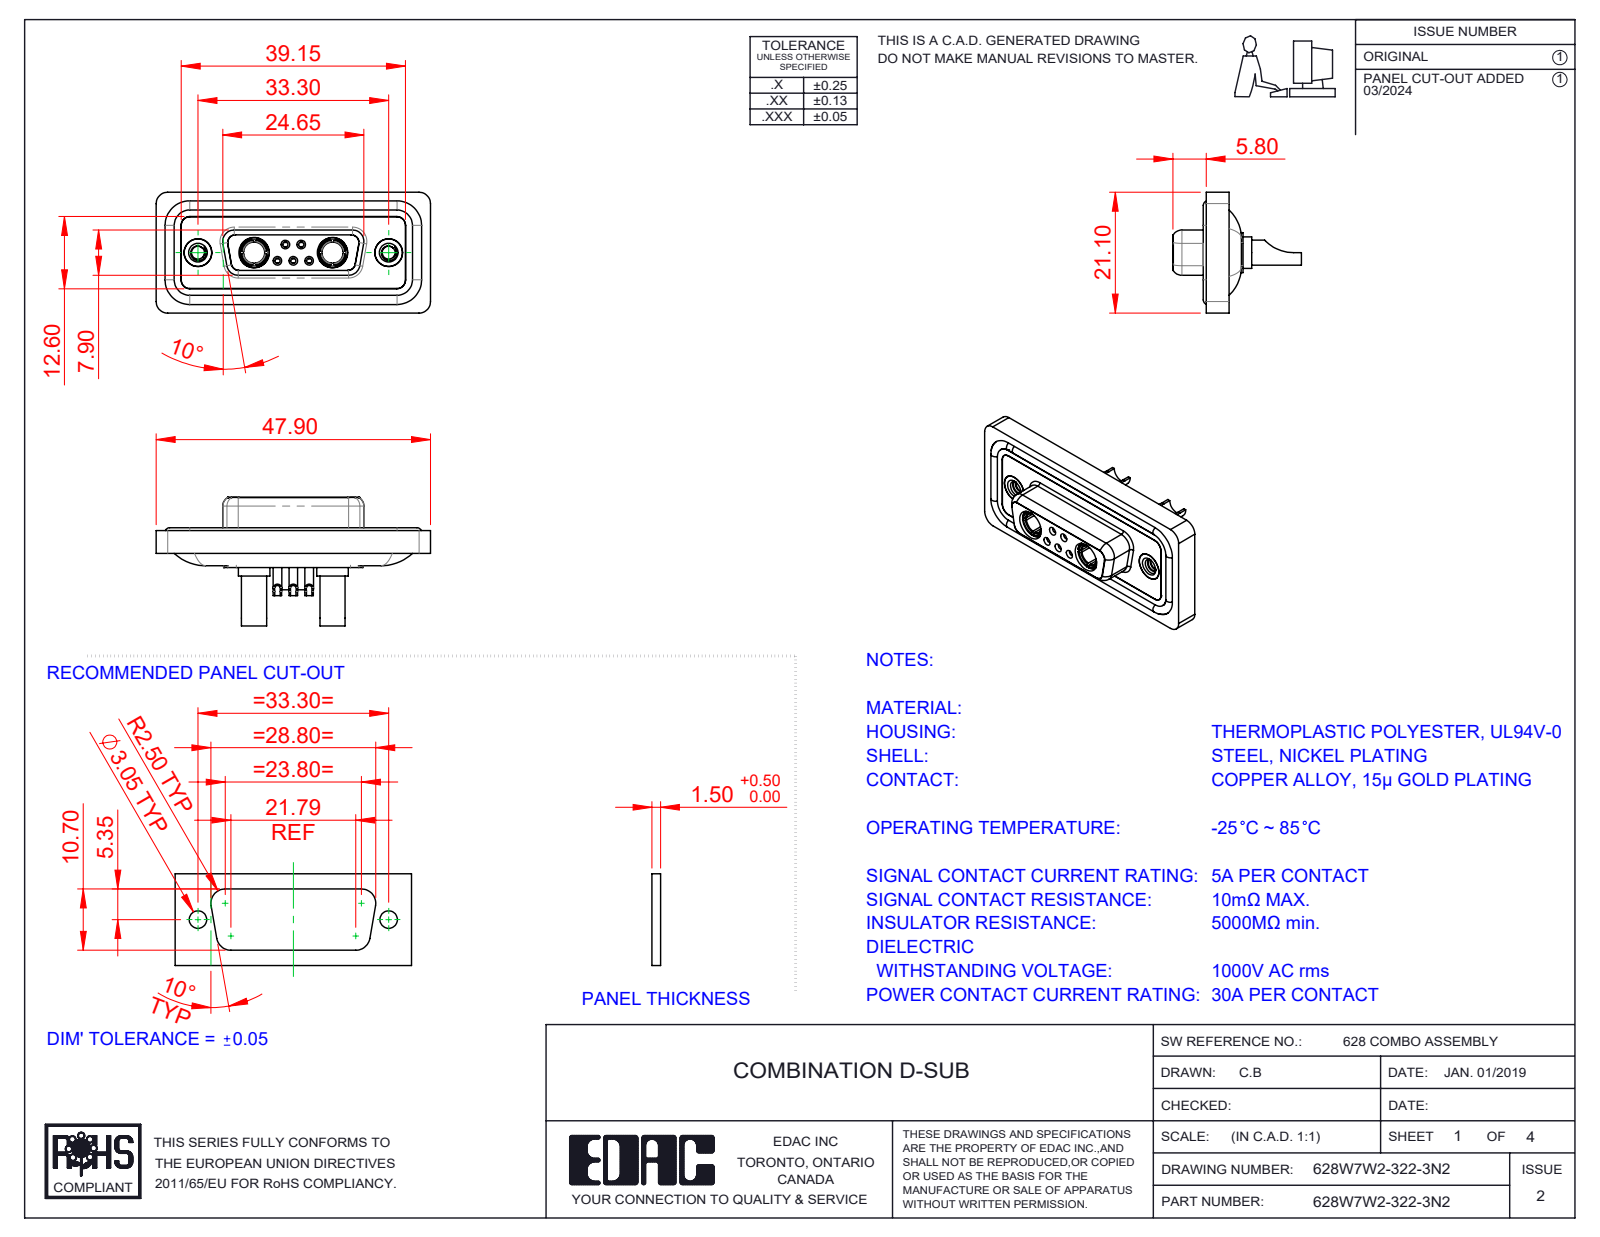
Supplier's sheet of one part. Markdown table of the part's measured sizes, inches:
| quantity | value |
| --- | --- |
| part name | 628Combo Shell Front_15 Contacts; 628Combo Shell Rear_15 Contacts; 628Combo Housing_7W2; 628Combo Contact Row 2_22 (+5 more) |
| STEP written by | SolidWorks 2023 (CONFIG_CONTROL_DESIGN) |
| units | inches |
| bodies | 16 solids, 821 faces (254 planar, 345 cylindrical, 222 other) |
| overall size | 1.886 × 0.884 × 0.831 |
| volume | 0.374 in³ |
| surface area | 15.74 in² |
| round holes (diameter × count) | 0.035 × 5, 0.039 × 5, 0.043 × 5, 0.059 × 5, 0.079 × 5, 0.191 × 4, 0.063 × 3, 0.067 × 2, 0.089 × 2, 0.138 × 2, 0.146 × 2, 0.157 × 2 |
| round bosses / shafts (diameter × count) | 0.063 × 6, 0.087 × 5, 0.217 × 2, 0.205 × 2, 0.195 × 2, 0.195 × 2, 0.189 × 2, 0.187 × 2 |
| partial cylindrical surfaces (radius × count) | 0.059 × 22, 0.079 × 20, 0.053 × 12, 0.063 × 8, 0.039 × 6, 0.01 × 4, 0.02 × 4, 0.024 × 4 |
| main face-to-face distances | 0.016, 0.063, 0.071, 0.02, 0.114, 0.043, 0.293, 0.222, 0.26, 0.278 |
| hole center spacings | 0.124, 0.109, 0.386, 0.925, 0.17, 0.17, 0.198, 0.198 |
